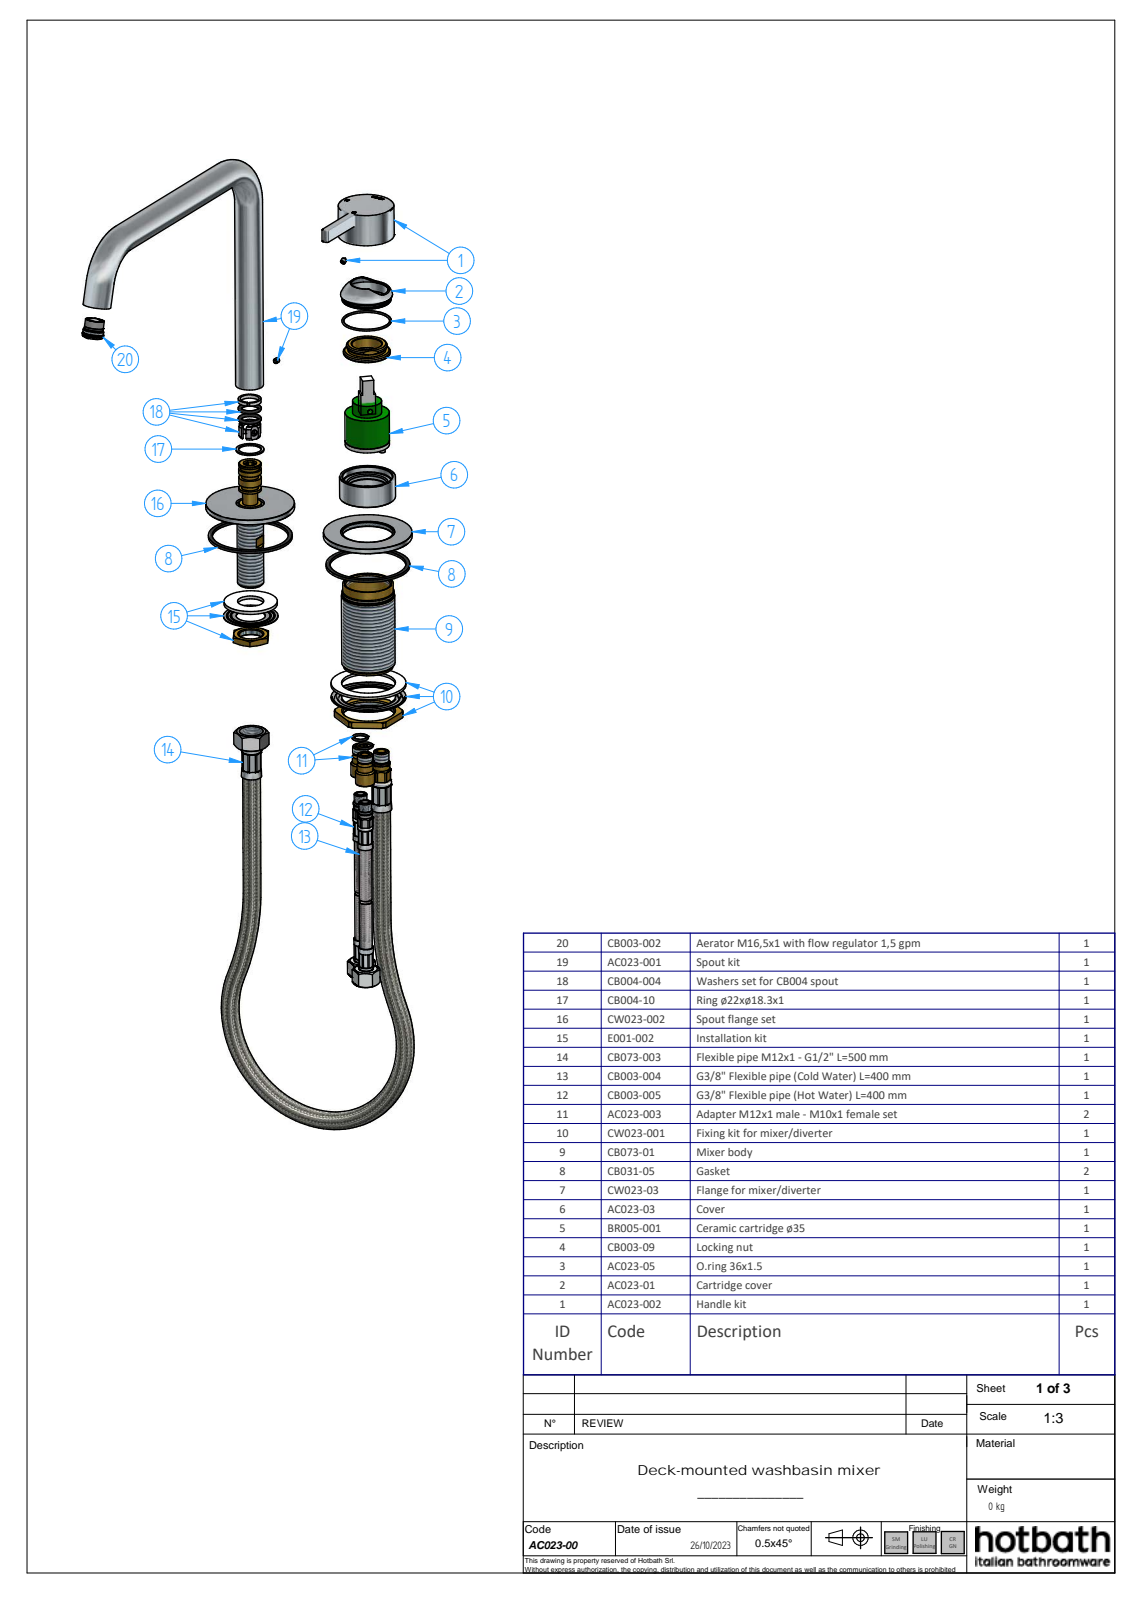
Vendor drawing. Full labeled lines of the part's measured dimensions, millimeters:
Part name (STEP PRODUCT): AC023-00; CW023-03_oa_0; CW023-002_oa_1; CW023-02 (+8 more)
STEP written by: Solid Edge (AUTOMOTIVE_DESIGN)
Units: millimetres
Bodies: 11 solids, 436 faces (192 planar, 91 cylindrical, 153 other)
Overall size (bounding box): 266.82 × 210.29 × 180
Volume: 97 296 mm³ · Surface area: 93 932 mm²
Round holes (diameter × count): ⌀18 ×3, ⌀3.24 ×1, ⌀4.2 ×1, ⌀8.5 ×1, ⌀11.03 ×1, ⌀12.2 ×1, ⌀14 ×1, ⌀14.58 ×1, ⌀16 ×1, ⌀18.75 ×1, ⌀22.2 ×1, ⌀30.38 ×1
Round bosses / shafts (diameter × count): ⌀22 ×3, ⌀70 ×2, ⌀57 ×1, ⌀44 ×1, ⌀43 ×1, ⌀38.6 ×1, ⌀36.2 ×1, ⌀25 ×1
Partial cylindrical surfaces — rounded edges, fillets, slot ends (radius × count): R0.5 ×13, R1 ×6, R1.5 ×5, R3 ×5, R2 ×3, R0.56 ×2, R0.73 ×2, R0.49 ×1
Main face-to-face distances: 2.3, 47, 44.7, 3.5, 0.5, 1.2, 48.2, 4, 2.5, 45.7
Hole centre spacings: 110, 184.59
